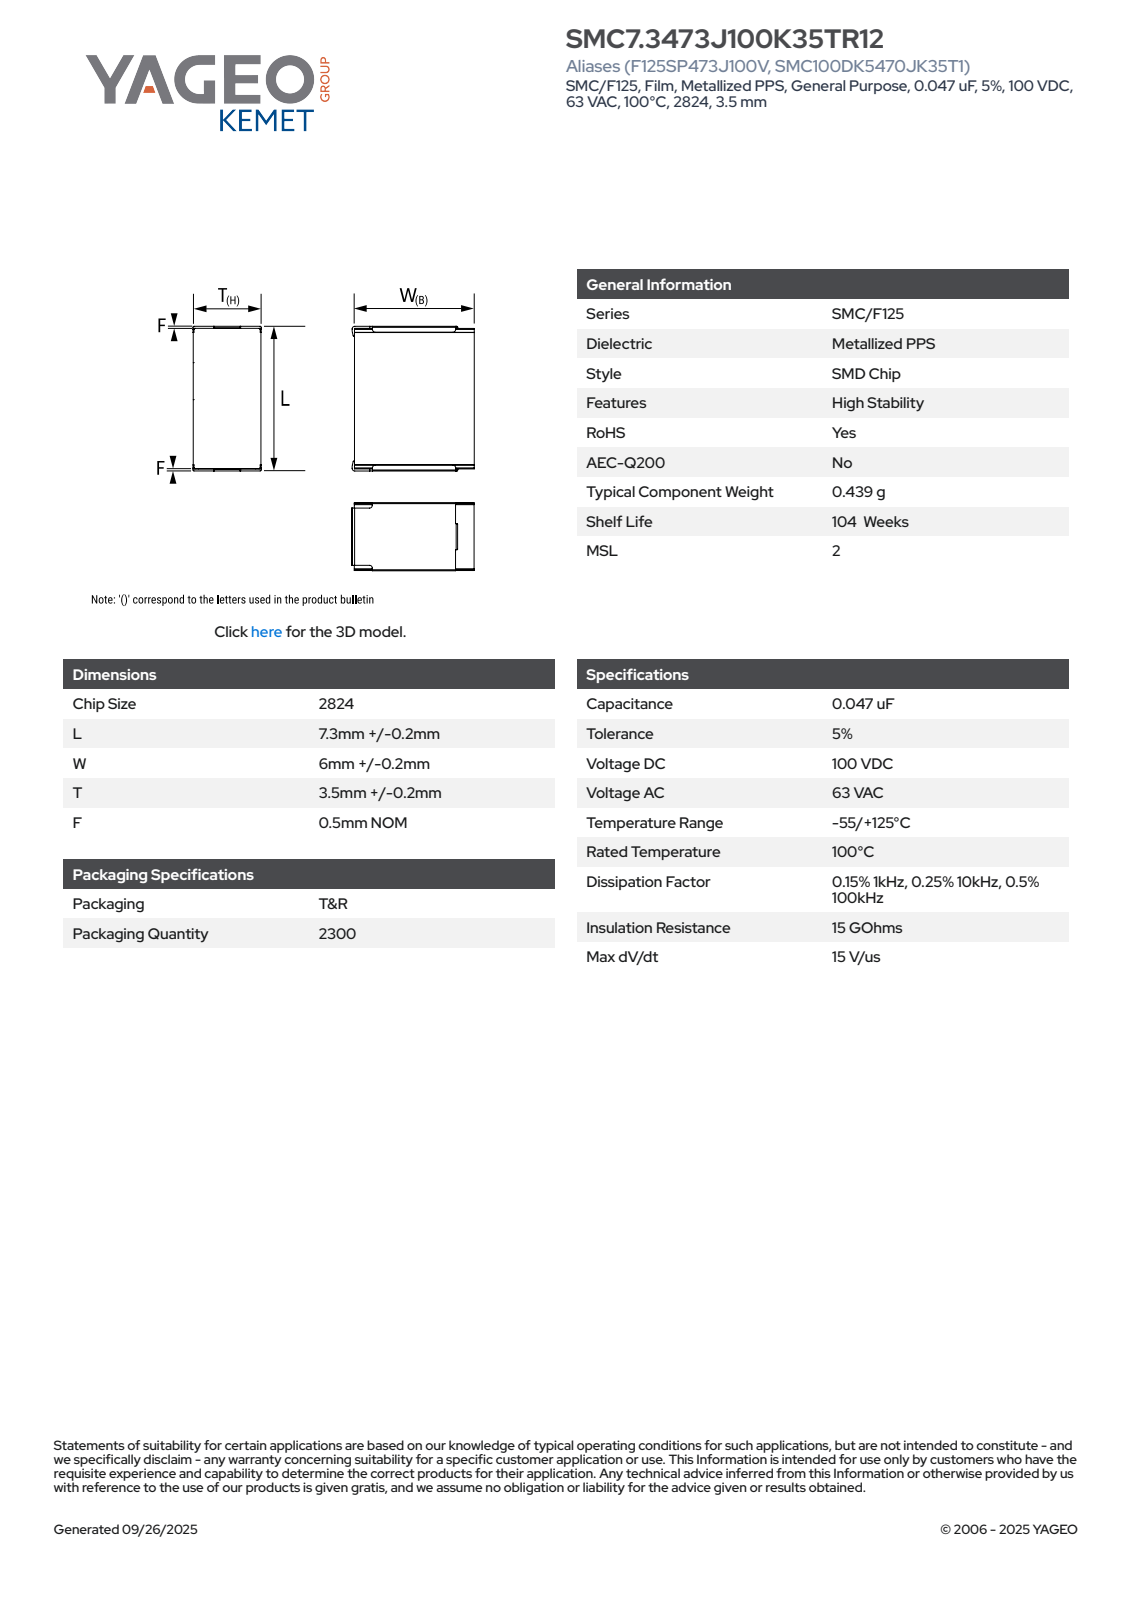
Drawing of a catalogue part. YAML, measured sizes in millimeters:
part_name: "CFS_KSTD_2824_L7.5W6.2T3.7F0.5"
step_written_by: "SolidWorks 2021 (AUTOMOTIVE_DESIGN)"
units: millimeters
bodies: {solids: 4, faces: 117, planar: 103, cylindrical: 14, other: 0}
overall_size: [7.5, 6.41, 3.89]
volume: 164
surface_area: 203
partial_cylinders:
  - {radius: 0.22, count: 10}
  - {radius: 0.26, count: 4}
face_to_face_distances: [3.7, 5.95, 7.5, 0.5, 7, 3.79, 6.5, 3.88, 6.41, 0.46]
